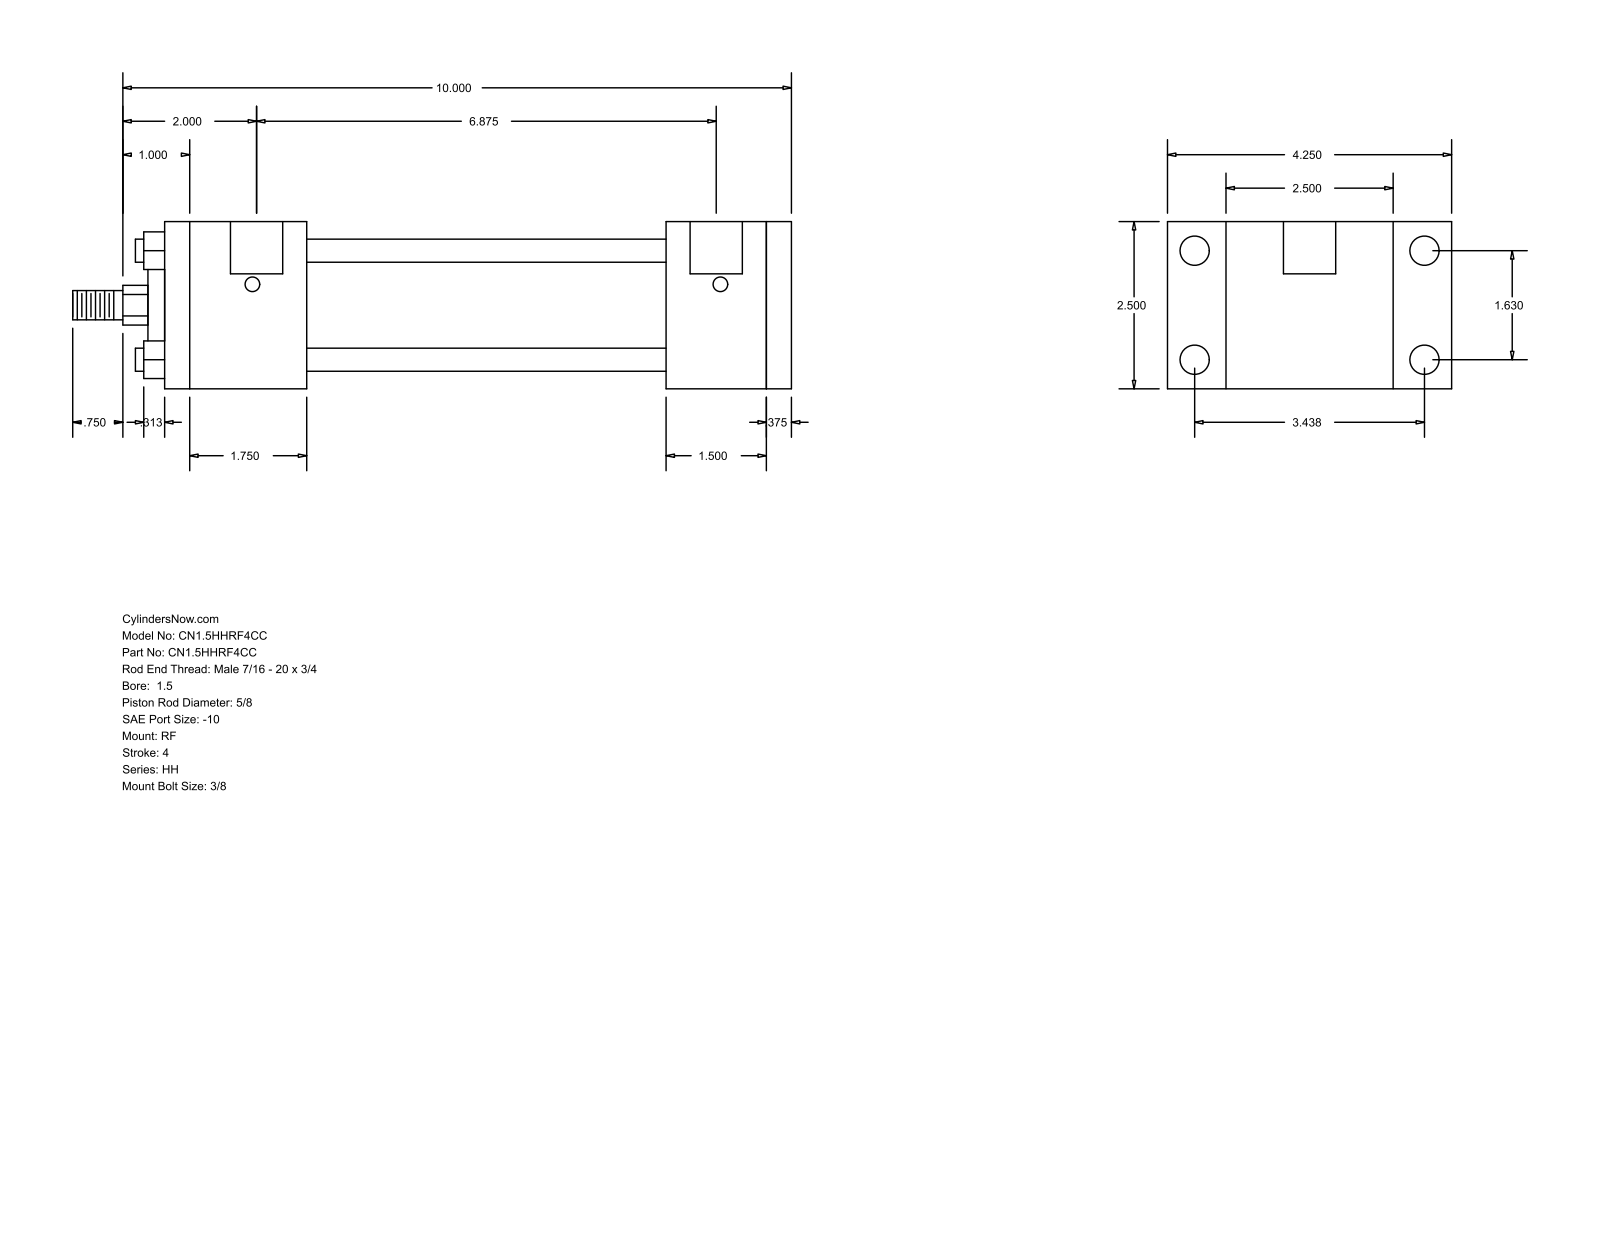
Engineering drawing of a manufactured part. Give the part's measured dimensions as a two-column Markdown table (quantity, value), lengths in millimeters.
| quantity | value |
| --- | --- |
| part name | HH_RF__0150_0.625 |
| STEP written by | GSSL Pune (CONFIG_CONTROL_DESIGN) |
| units | millimeters |
| bodies | 0 solids, 92 faces (64 planar, 28 cylindrical, 0 other) |
| overall size | 273.05 × 107.95 × 63.5 |
| round holes (diameter × count) | 5.56 × 4, 11.13 × 4, 19.84 × 2 |
| round bosses / shafts (diameter × count) | 8.76 × 4, 44.45 × 1, 28.57 × 1, 15.88 × 1, 11.11 × 1 |
| partial cylindrical surfaces (radius × count) | 7.54 × 1 |
| main face-to-face distances | 63.5, 238.12, 9.53, 228.59, 53.97, 190.5, 136.53, 174.62, 184.15, 38.09 |
| hole center spacings | 41.4, 87.32, 96.64, 177.8, 1.58, 1.59, 174.63, 176.21 |
